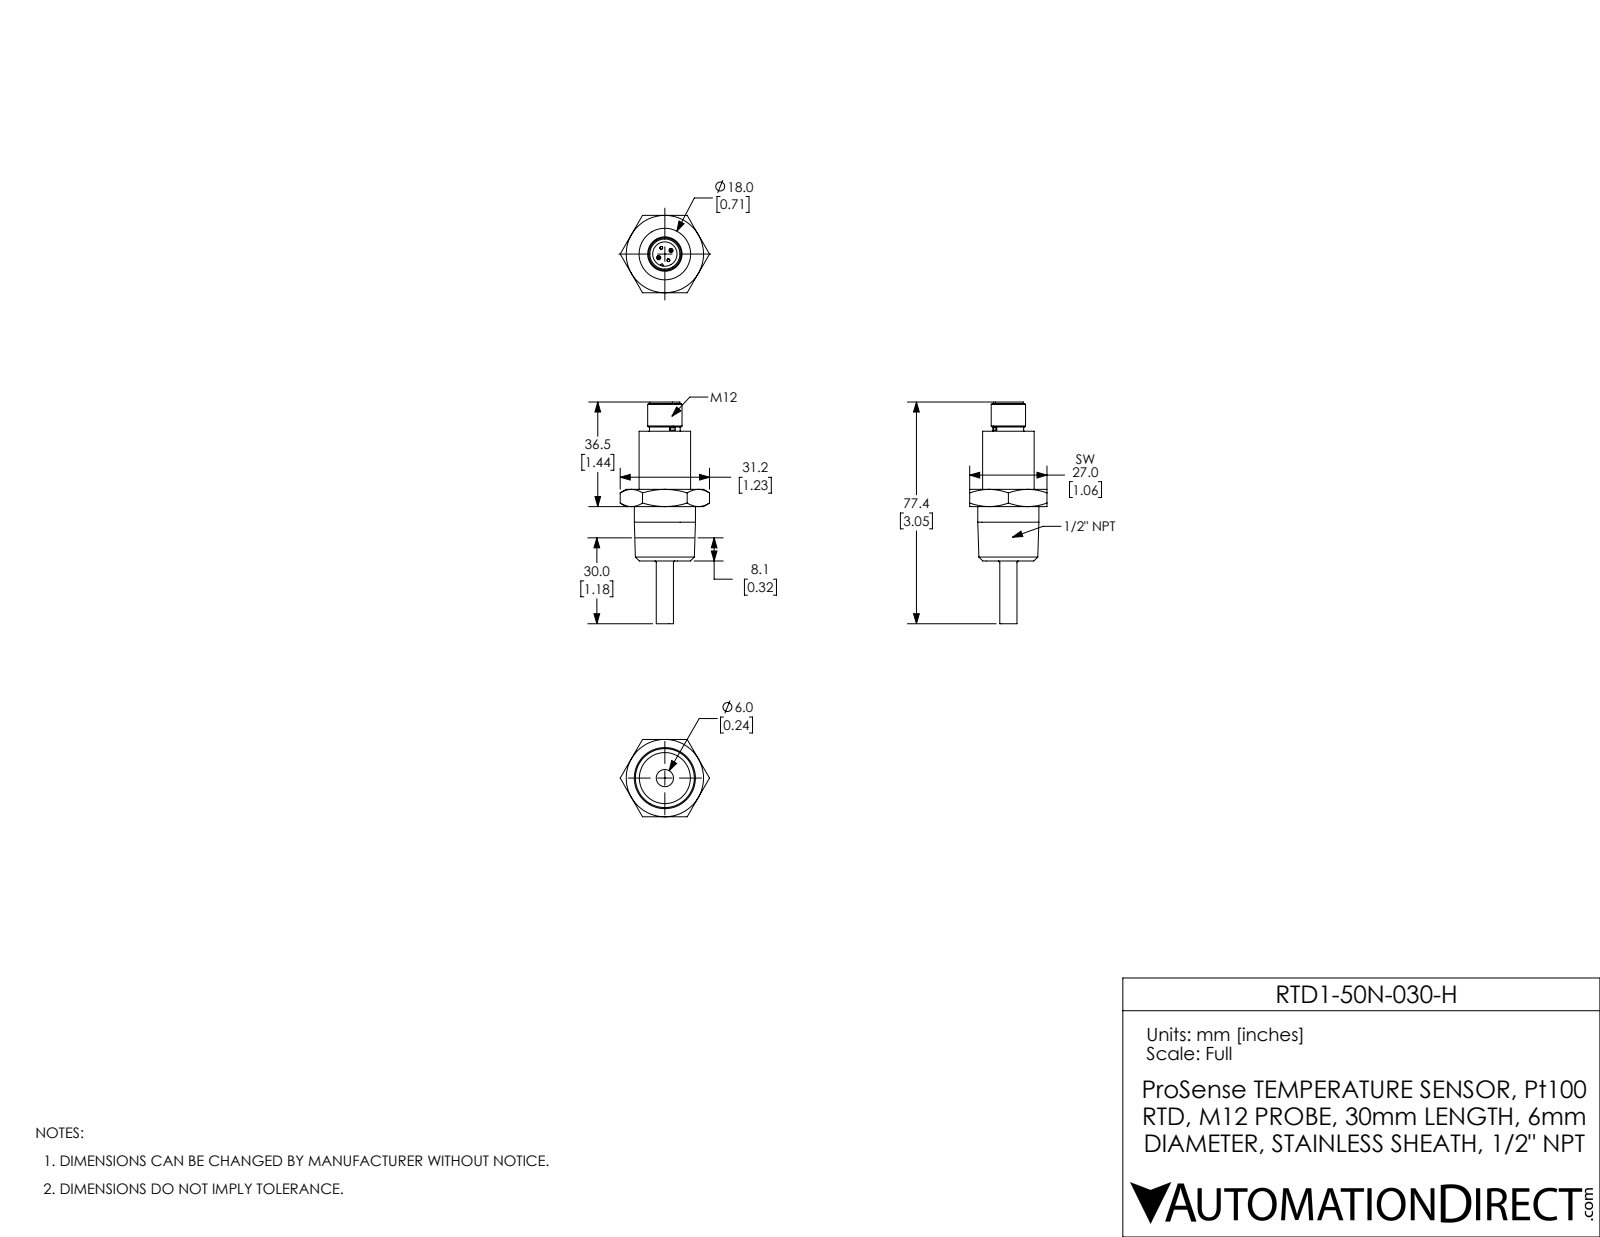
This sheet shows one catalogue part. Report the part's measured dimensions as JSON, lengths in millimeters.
{"part_name": "RTD1-50N-030-H", "step_written_by": "SolidWorks 2017 (AUTOMOTIVE_DESIGN)", "units": "millimeters", "bodies": {"solids": 1, "faces": 94, "planar": 32, "cylindrical": 23, "other": 39}, "overall_size": [77.4, 31.2, 27], "volume_mm3": 16680, "surface_area_mm2": 5200, "round_holes": [[8.5, 1]], "round_bosses_or_shafts": [[1, 4], [21.3, 1], [18, 1], [12, 1], [10.7, 1], [10.5, 1], [6, 1]], "partial_cylinders_radius": [[0.4, 1]], "face_to_face_distances": [27, 6, 19, 25, 45.3, 26.3, 20.3, 46.5, 27.5, 21.5]}
